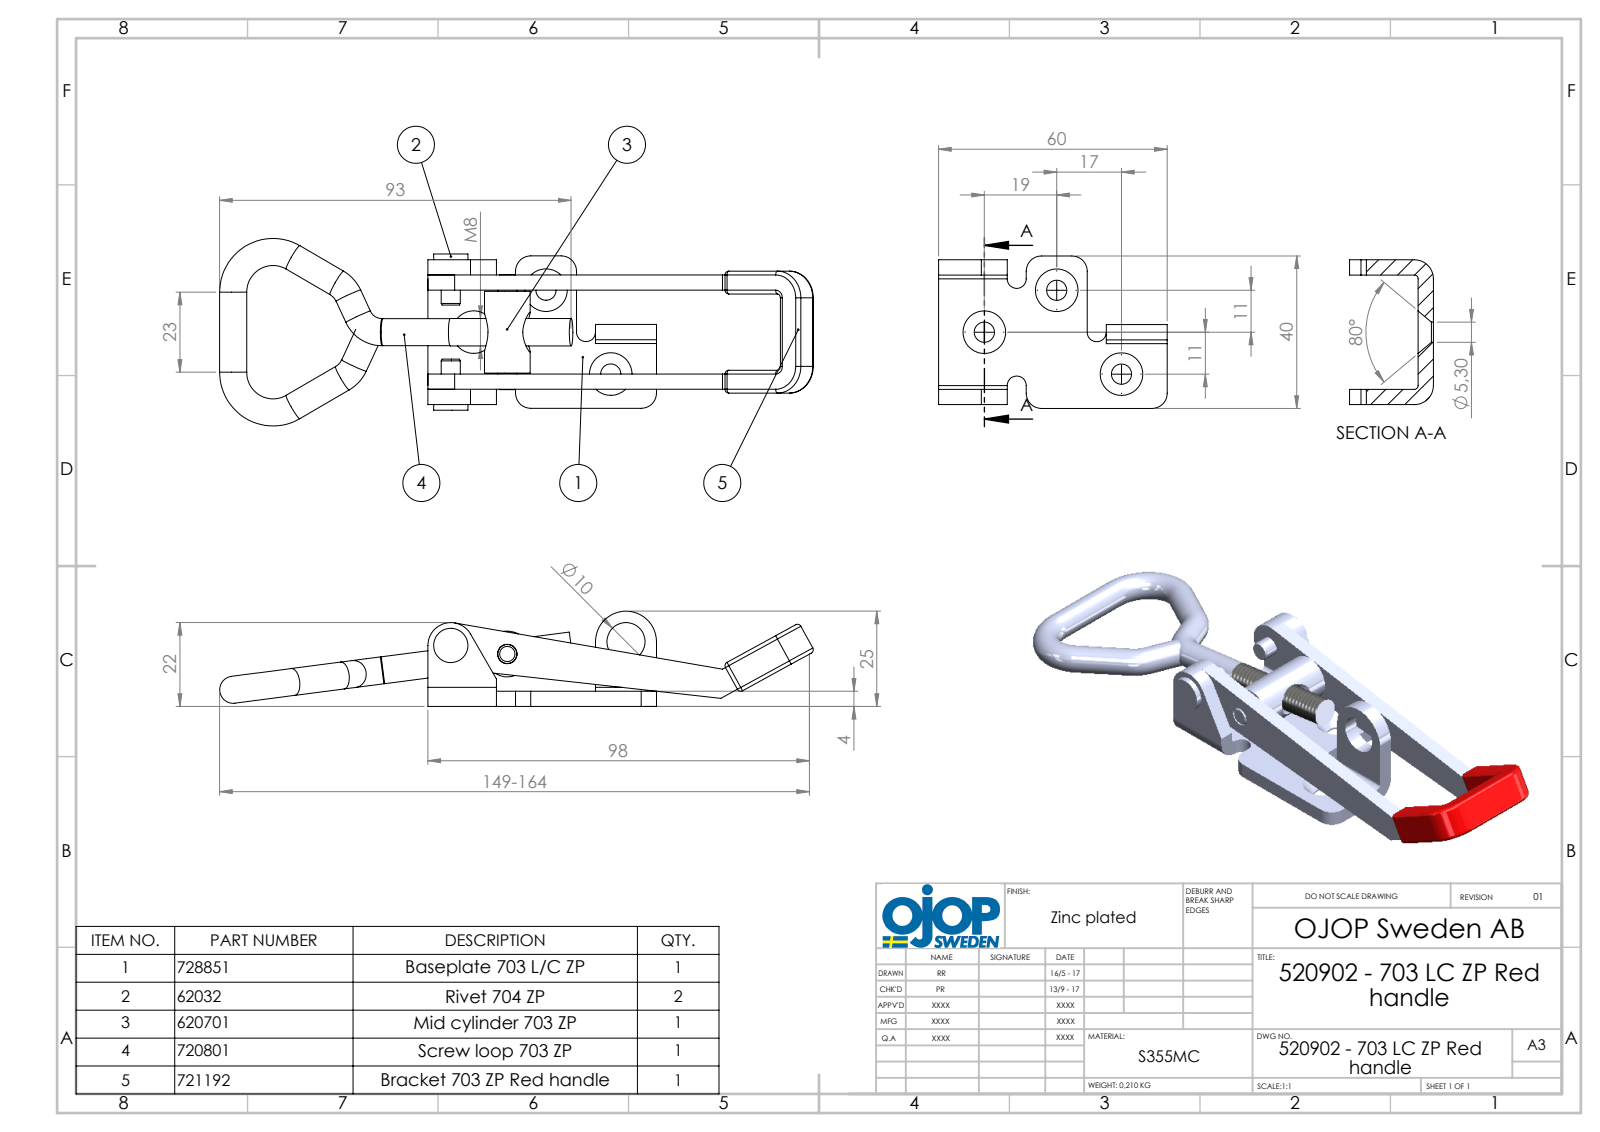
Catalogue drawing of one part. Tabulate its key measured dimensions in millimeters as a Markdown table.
| quantity | value |
| --- | --- |
| part name | 520902 - 703 LC ZP Red handle; 703 -bygelrödplast; 703 - Skruvögla; 703 - Rulle (+2 more) |
| STEP written by | SolidWorks 2015 (AUTOMOTIVE_DESIGN) |
| units | millimeters |
| bodies | 6 solids, 213 faces (66 planar, 93 cylindrical, 54 other) |
| overall size | 155.16 × 49.4 × 31.52 |
| volume | 28 204 mm³ |
| surface area | 18 843 mm² |
| round holes (diameter × count) | 5.3 × 3, 5.1 × 2, 7.2 × 1, 7.7 × 1, 10 × 1 |
| round bosses / shafts (diameter × count) | 7 × 4, 5 × 2, 12 × 1, 9 × 1, 7.7 × 1 |
| partial cylindrical surfaces (radius × count) | 1 × 23, 4 × 4, 2.5 × 3, 5 × 3, 7 × 2, 6 × 1, 8 × 1 |
| main face-to-face distances | 4, 26, 30, 22, 6, 17, 13, 9, 21, 10 |
| hole center spacings | 15.01, 21.95, 27.8, 31.04, 37.64, 46.01 |
